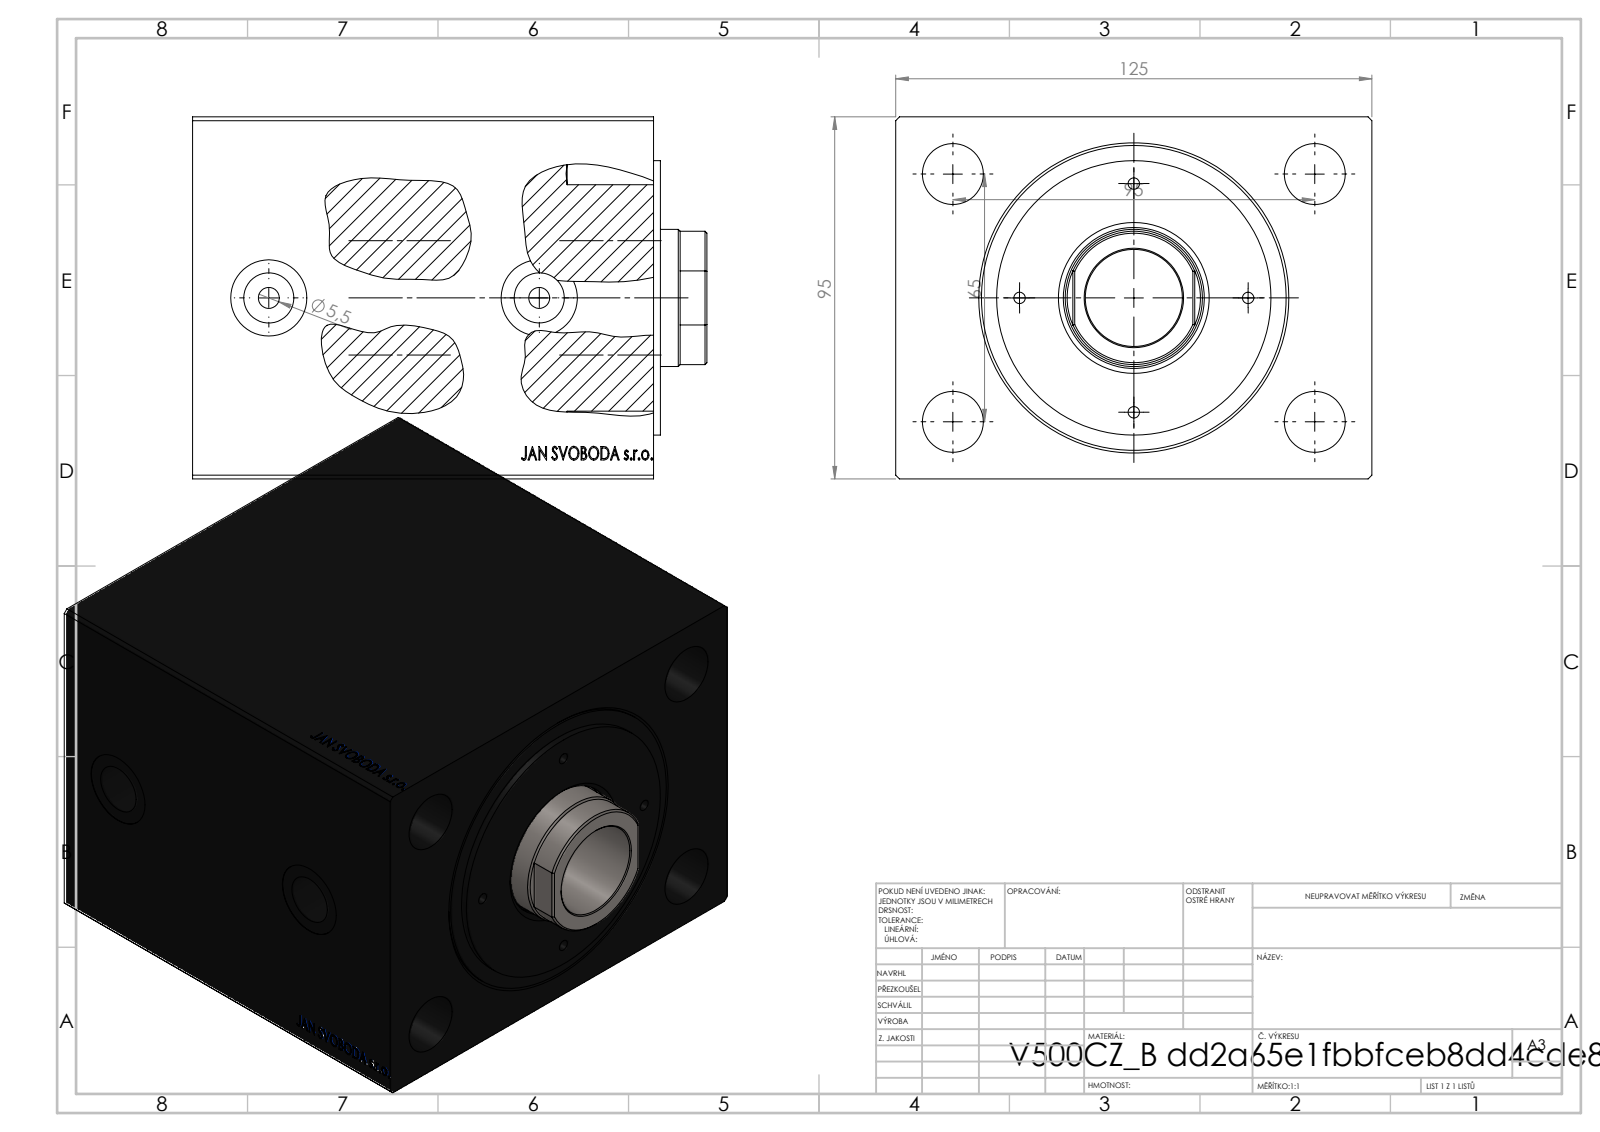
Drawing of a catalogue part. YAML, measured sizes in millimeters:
part_name: "V500CZ; V500CZ_B_VC"
step_written_by: "SolidWorks 2019 (CONFIG_CONTROL_DESIGN)"
units: millimeters
bodies: {solids: 3, faces: 874, planar: 400, cylindrical: 58, other: 416}
overall_size: [135, 125, 95]
volume: 1434000
surface_area: 180916
round_holes:
  - {diameter: 3, count: 4}
  - {diameter: 16, count: 4}
  - {diameter: 5.5, count: 2}
  - {diameter: 13.16, count: 2}
  - {diameter: 20, count: 2}
  - {diameter: 25.5, count: 1}
  - {diameter: 36, count: 1}
  - {diameter: 37, count: 1}
  - {diameter: 63, count: 1}
  - {diameter: 80, count: 1}
round_bosses_or_shafts:
  - {diameter: 72, count: 1}
partial_cylinders:
  - {radius: 17.5, count: 1}
face_to_face_distances: [95, 125, 121, 102.5, 18.5, 91, 11.5, 30, 1.8, 92.8]
hole_center_spacings: [30, 36.91, 42.43, 47.57, 57.55, 78.5, 84.04, 60]
